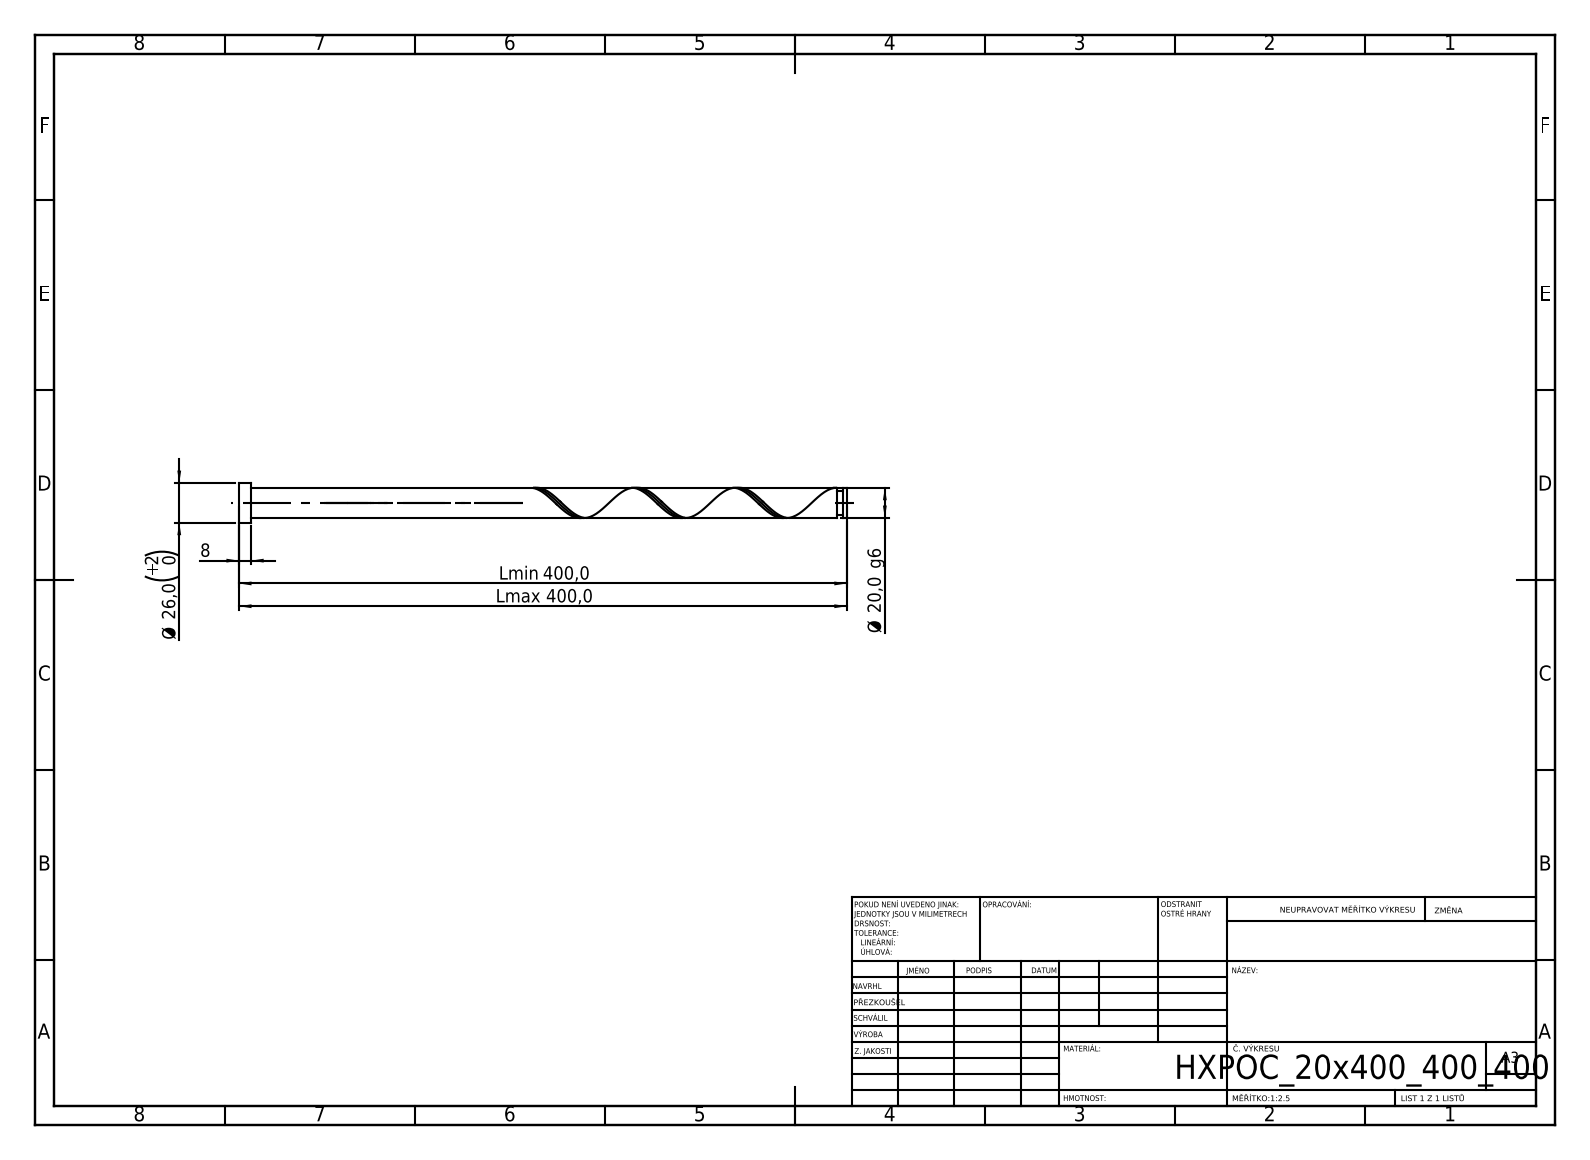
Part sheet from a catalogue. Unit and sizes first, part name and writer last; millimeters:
Units: millimetres
Overall size (bounding box): 400 × 26 × 26
Round bosses / shafts (diameter × count): ⌀26 ×1, ⌀20 ×1, ⌀16 ×1
Main face-to-face distances: 400, 8, 392, 397.52, 389.52, 2.48, 393.52, 385.52, 4, 6.48
Volume: 125 742 mm³ · Surface area: 27 111 mm²
Bodies: 1 solid, 21 faces (6 planar, 14 cylindrical, 1 other)
STEP written by: SolidWorks 2019 (CONFIG_CONTROL_DESIGN)
